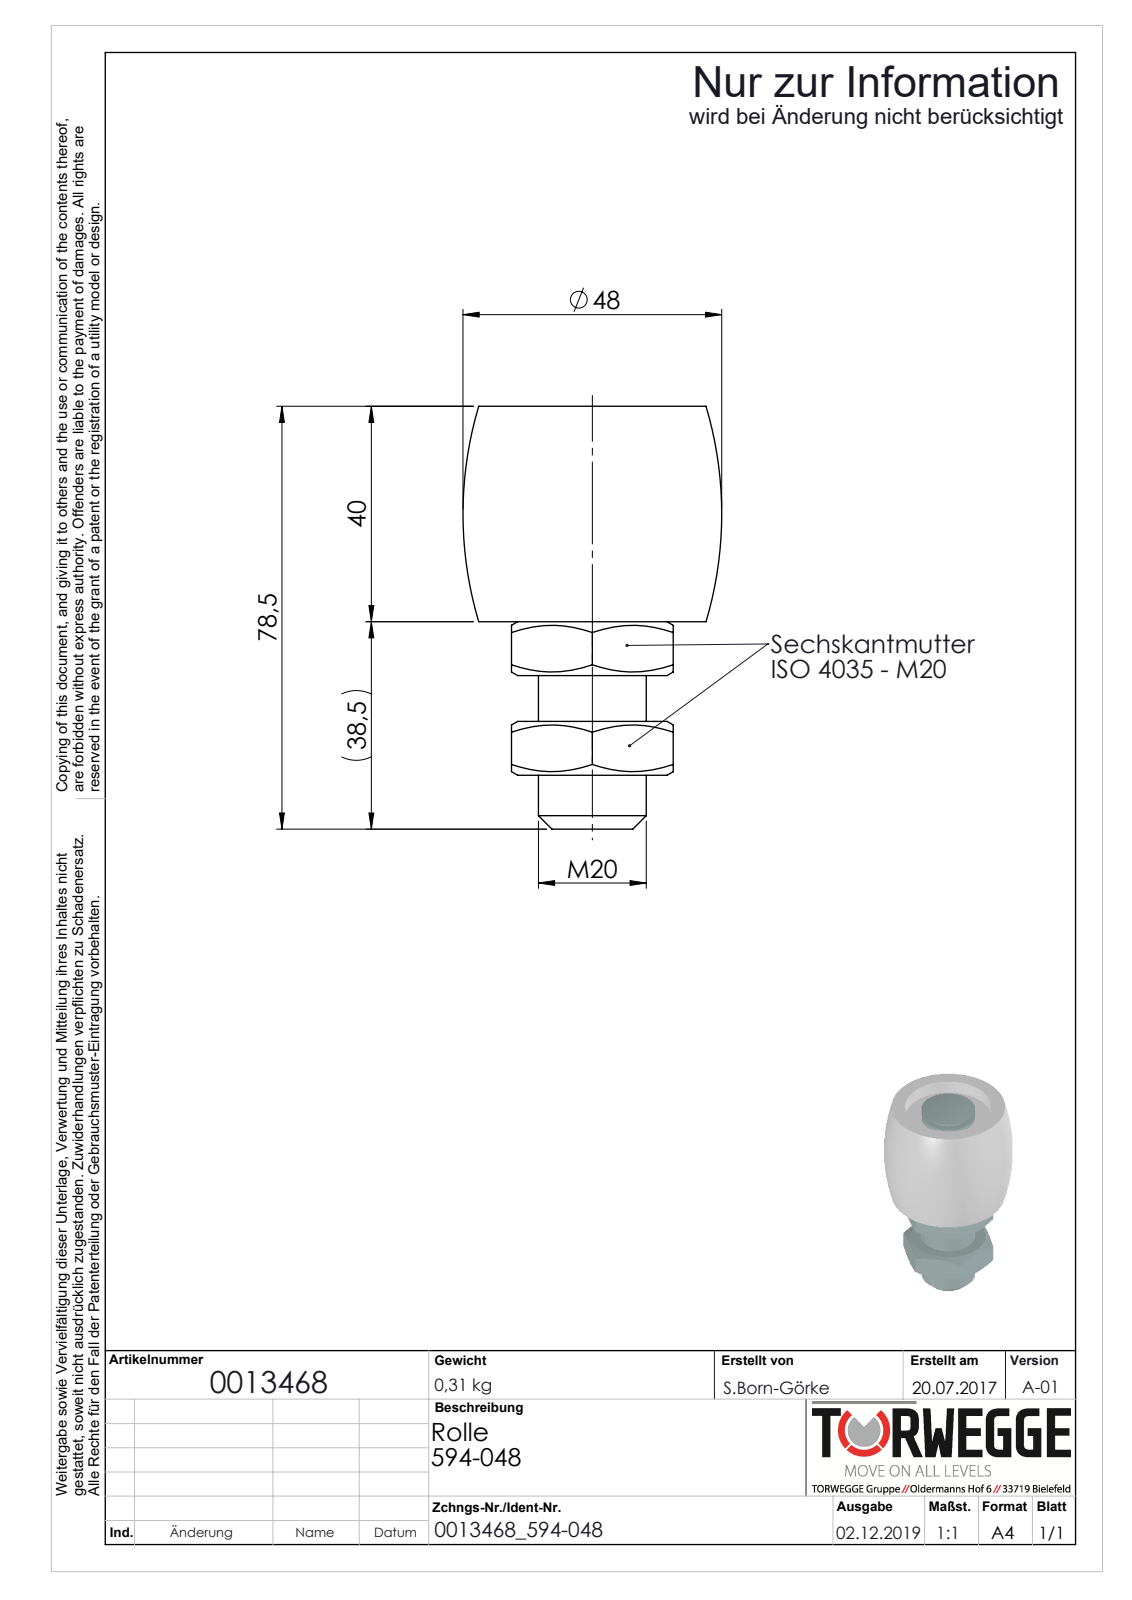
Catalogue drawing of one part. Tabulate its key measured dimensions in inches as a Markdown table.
| quantity | value |
| --- | --- |
| part name | 0013468_594-048_(A-01) |
| STEP written by | SolidWorks 2018 (AUTOMOTIVE_DESIGN) |
| units | inches |
| bodies | 6 solids, 71 faces (26 planar, 20 cylindrical, 25 other) |
| overall size | 3.091 × 1.89 × 1.89 |
| volume | 5.434 in³ |
| surface area | 37.81 in² |
| round holes (diameter × count) | 0.591 × 1, 0.681 × 1, 0.799 × 1, 0.827 × 1, 1.26 × 1 |
| round bosses / shafts (diameter × count) | 1.457 × 1, 1.102 × 1, 0.787 × 1, 0.587 × 1 |
| main face-to-face distances | 0.728, 1.181, 0.394, 0.13, 0.598, 2.303, 2.173, 1.575, 2.157, 2.028 |
